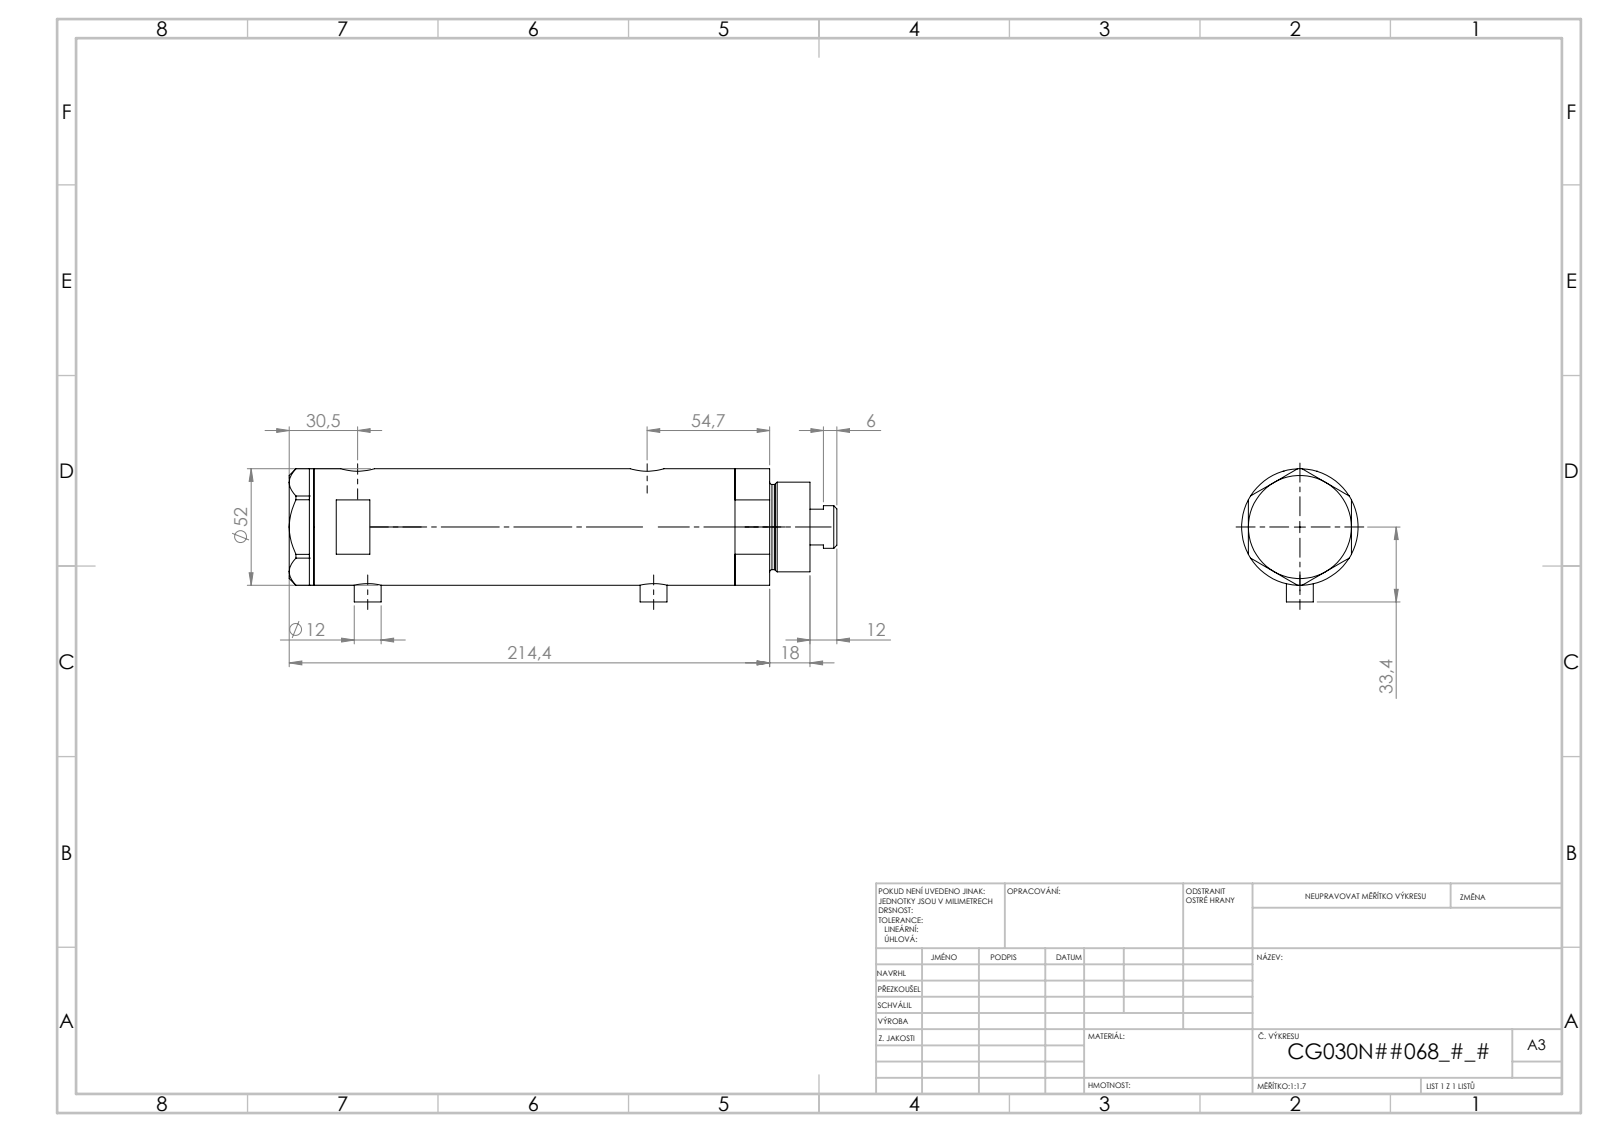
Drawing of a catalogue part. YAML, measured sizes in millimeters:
part_name: "V270CG_BACK; V270CG_VC; V270CG_FRONT; V270CG_MIDDLE"
step_written_by: "SolidWorks 2019 (CONFIG_CONTROL_DESIGN)"
units: millimeters
bodies: {solids: 4, faces: 140, planar: 67, cylindrical: 53, other: 20}
overall_size: [217.02, 53.1, 52]
volume: 385228
surface_area: 86879
round_holes:
  - {diameter: 5, count: 2}
  - {diameter: 9.73, count: 2}
  - {diameter: 12.5, count: 2}
  - {diameter: 15, count: 2}
  - {diameter: 6.5, count: 1}
  - {diameter: 20, count: 1}
  - {diameter: 21.5, count: 1}
  - {diameter: 30, count: 1}
  - {diameter: 33, count: 1}
  - {diameter: 44, count: 1}
round_bosses_or_shafts:
  - {diameter: 12, count: 2}
  - {diameter: 52, count: 1}
  - {diameter: 40, count: 1}
  - {diameter: 38, count: 1}
  - {diameter: 19, count: 1}
face_to_face_distances: [121.54, 23.8, 97.74, 11, 34.8, 132.54, 46, 168.94, 157.94, 134.14]
hole_center_spacings: [2.9, 4.5, 94.75, 97.65, 99.25, 102.15, 2.89, 2.91]
